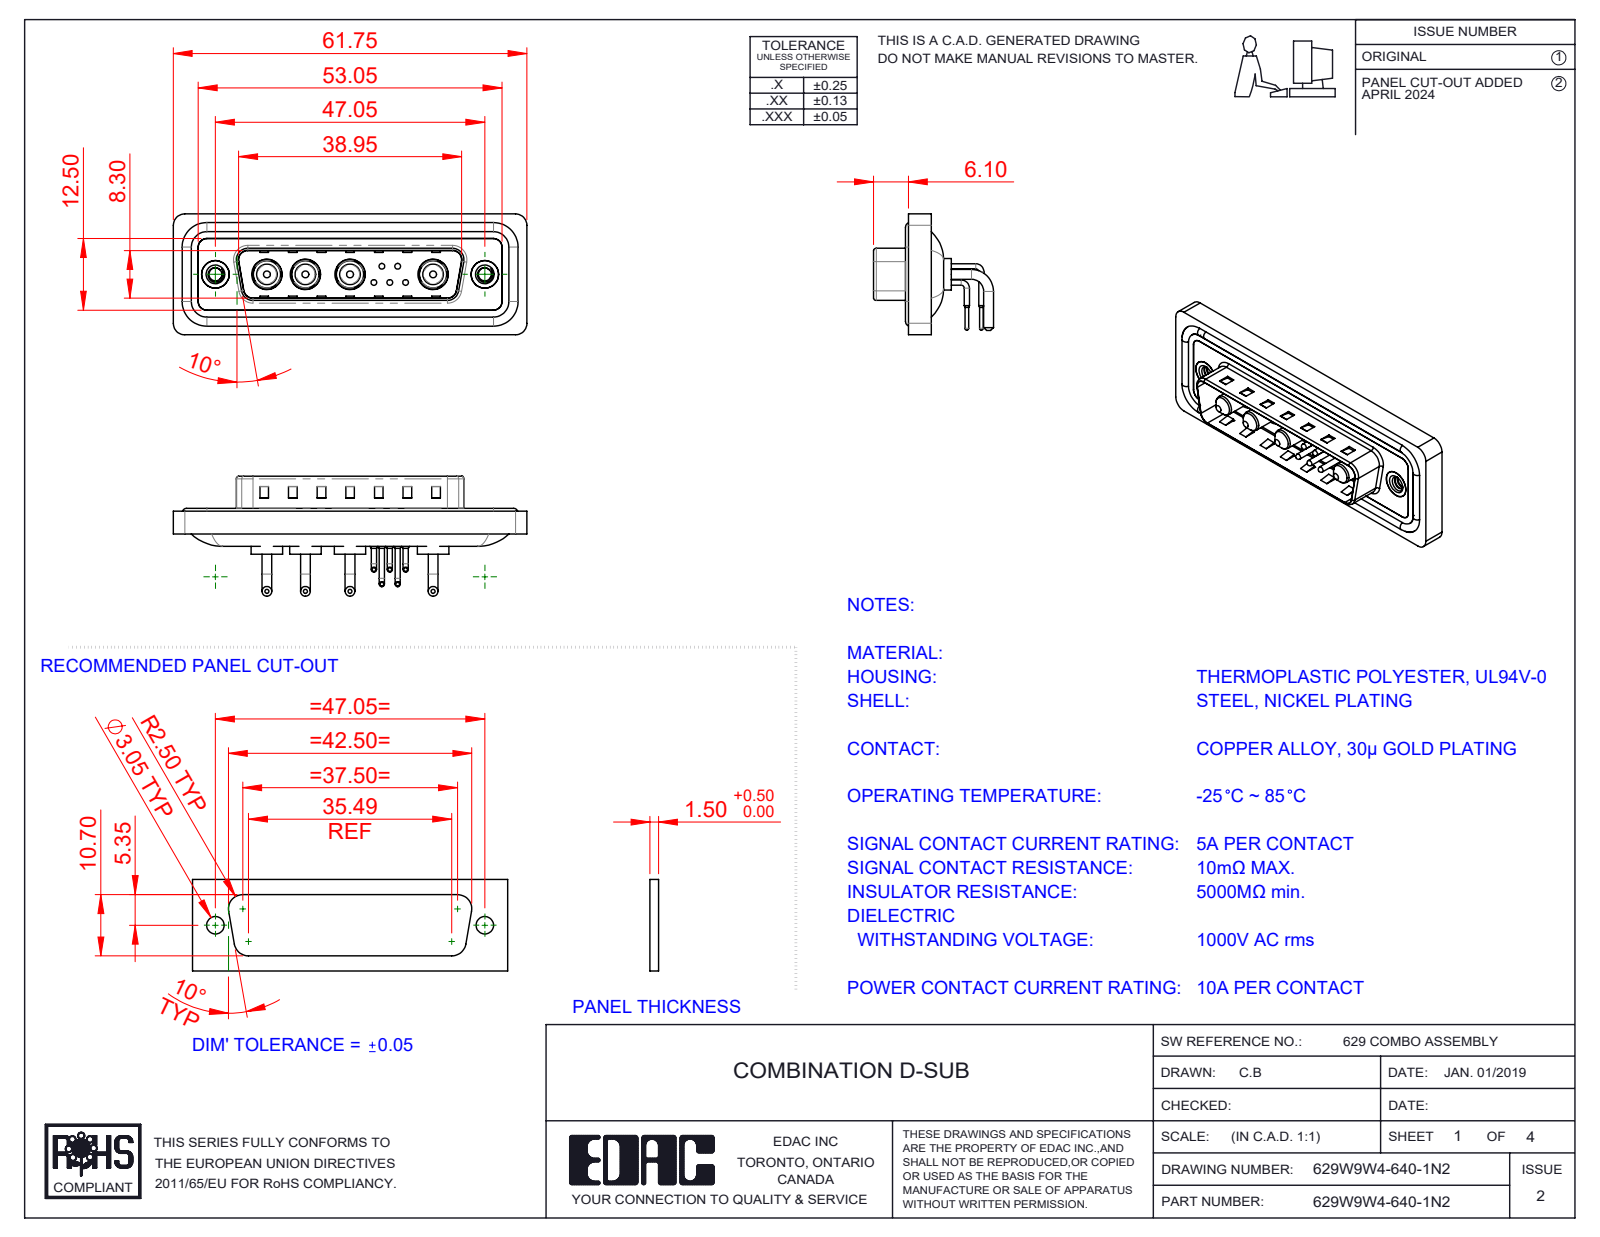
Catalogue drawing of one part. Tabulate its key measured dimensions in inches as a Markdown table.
| quantity | value |
| --- | --- |
| part name | Power Pin_10A RA; 629Combo Contact Row 1; 629Combo Waterproof Housing_25 Contacts; 629Combo Shell Front_25 Contacts (+5 more) |
| STEP written by | SolidWorks 2023 (CONFIG_CONTROL_DESIGN) |
| units | inches |
| bodies | 20 solids, 1205 faces (569 planar, 452 cylindrical, 184 other) |
| overall size | 2.431 × 0.831 × 0.825 |
| volume | 0.457 in³ |
| surface area | 18.87 in² |
| round holes (diameter × count) | 0.03 × 5, 0.063 × 5, 0.079 × 5, 0.191 × 4, 0.209 × 4, 0.089 × 2, 0.157 × 2, 0.189 × 2, 0.197 × 2 |
| round bosses / shafts (diameter × count) | 0.035 × 10, 0.067 × 8, 0.059 × 5, 0.039 × 5, 0.026 × 5, 0.217 × 4, 0.205 × 4, 0.187 × 4 |
| partial cylindrical surfaces (radius × count) | 0.059 × 18, 0.079 × 18, 0.02 × 8, 0.063 × 8, 0.04 × 5, 0.01 × 4, 0.024 × 4, 0.026 × 4 |
| main face-to-face distances | 0.016, 0.114, 0.031, 0.161, 0.043, 0.177, 0.083, 0.059, 0.063, 0.122 |
| hole center spacings | 0.124, 0.109, 0.198, 0.571, 0.109, 0.173, 0.174, 0.197 |
